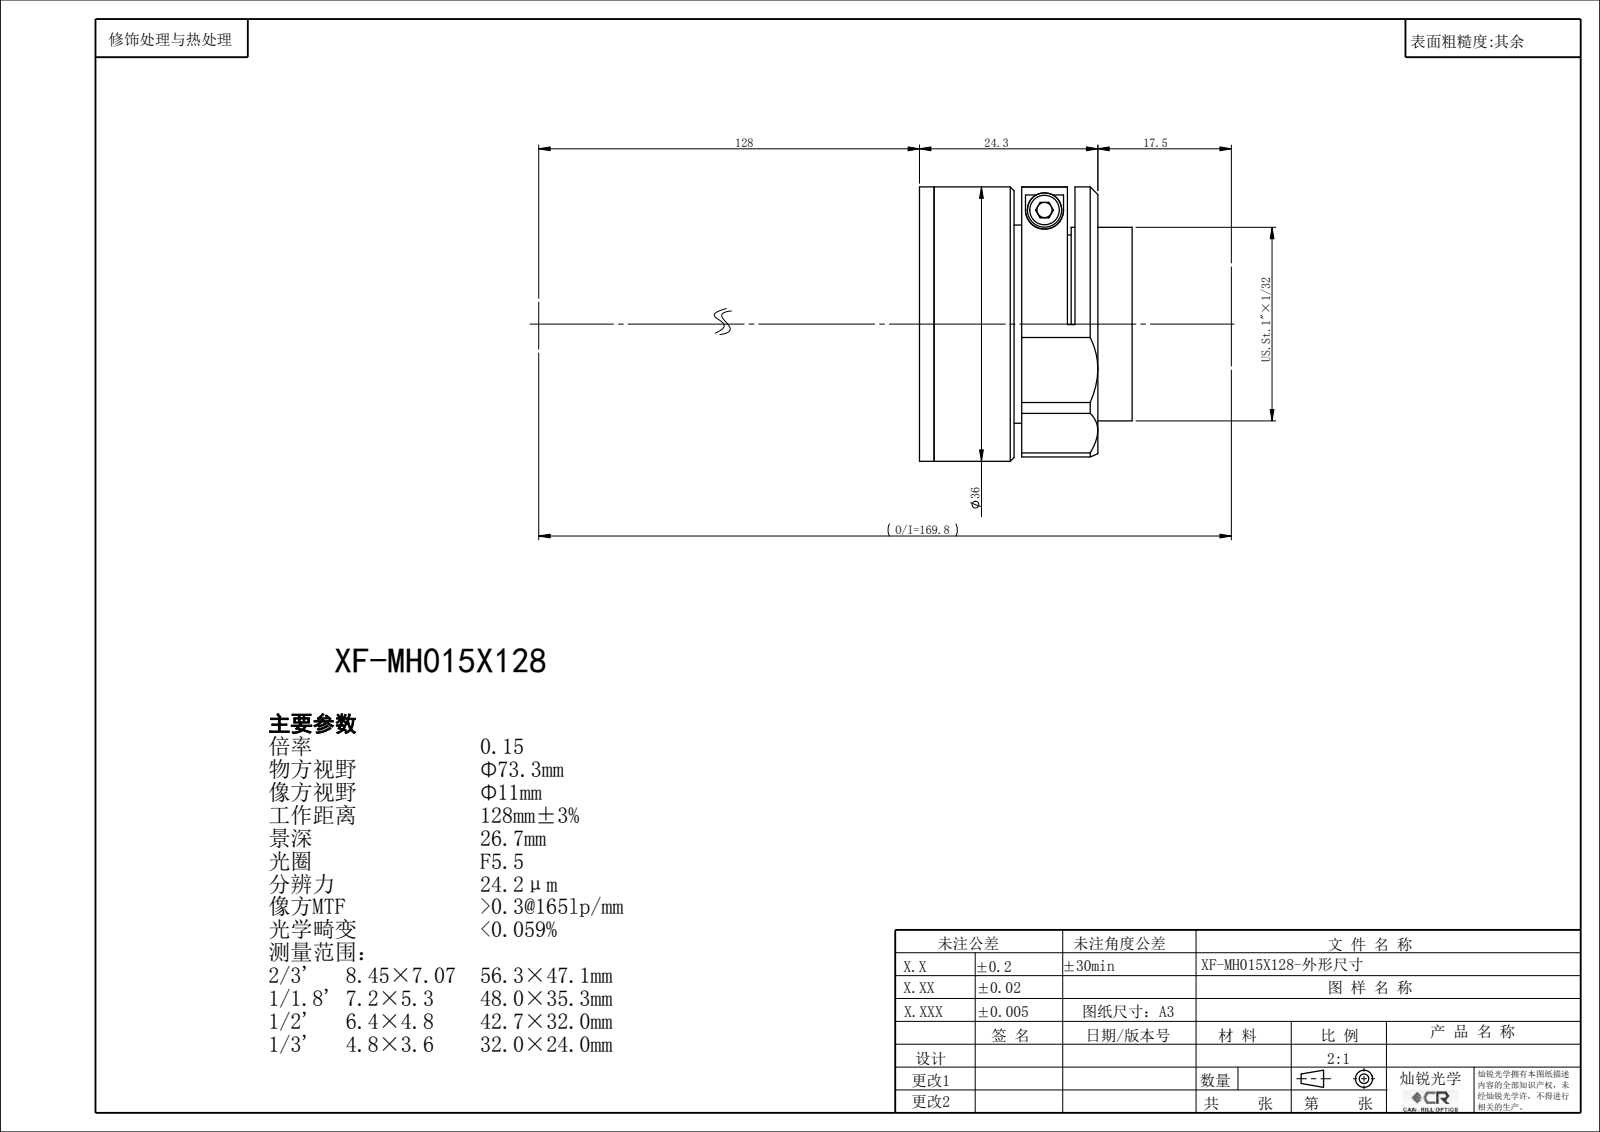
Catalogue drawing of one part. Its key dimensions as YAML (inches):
part_name: "XF-MH015X128"
step_written_by: "SolidWorks 2022 (CONFIG_CONTROL_DESIGN)"
units: inches
bodies: {solids: 0, faces: 111, planar: 51, cylindrical: 50, other: 10}
overall_size: [1.417, 1.417, 1.113]
round_holes:
  - {diameter: 0.098, count: 3}
  - {diameter: 0.276, count: 1}
  - {diameter: 0.331, count: 1}
  - {diameter: 0.394, count: 1}
  - {diameter: 0.472, count: 1}
  - {diameter: 0.551, count: 1}
  - {diameter: 0.63, count: 1}
  - {diameter: 0.709, count: 1}
  - {diameter: 0.787, count: 1}
  - {diameter: 0.846, count: 1}
  - {diameter: 0.866, count: 1}
  - {diameter: 0.945, count: 1}
round_bosses_or_shafts:
  - {diameter: 1.417, count: 1}
  - {diameter: 1.339, count: 1}
  - {diameter: 1.142, count: 1}
  - {diameter: 1, count: 1}
  - {diameter: 0.354, count: 1}
face_to_face_distances: [0.075, 0.88, 0.956, 0.079, 0.039, 0.059, 0.896, 0.821, 0.823, 0.157]
